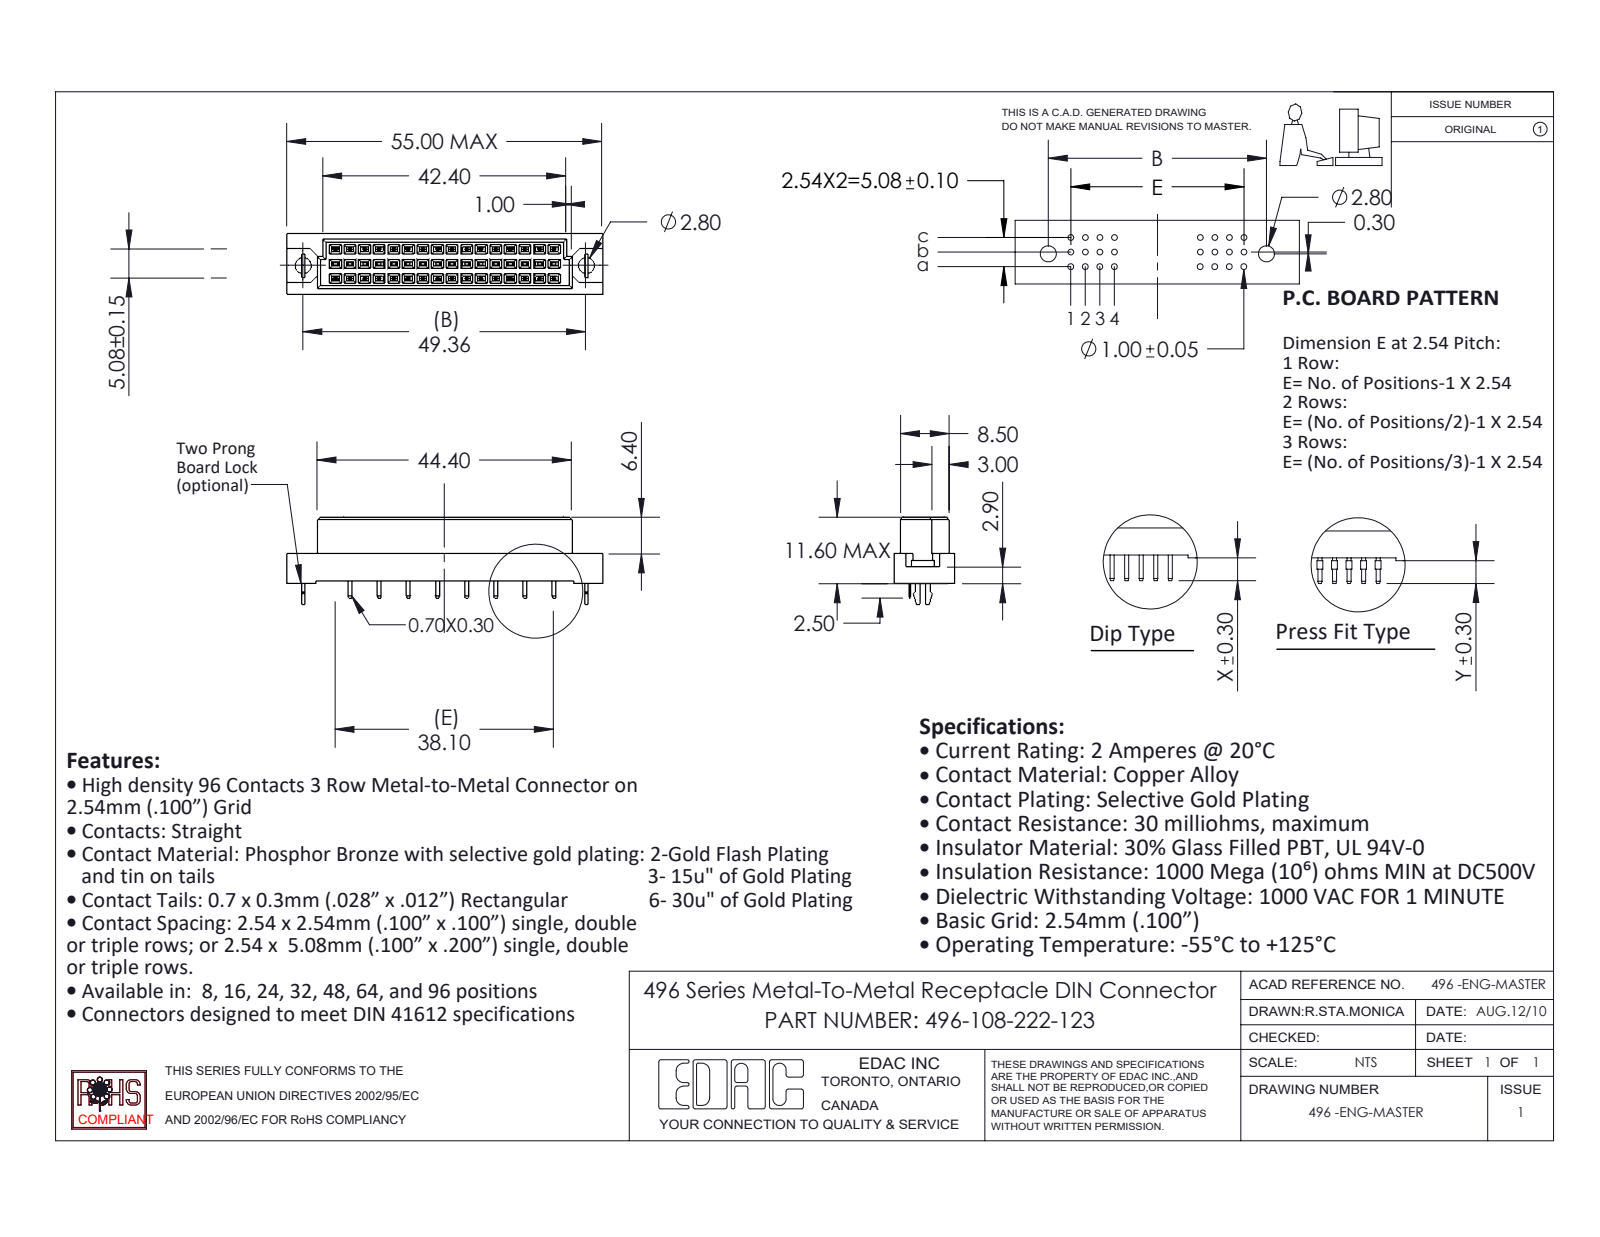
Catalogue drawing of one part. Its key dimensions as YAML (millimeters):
part_name: "496 Part_48; 496-108-222-123; 496-290_22; 496 Bore-lock"
step_written_by: "SolidWorks 2020 (CONFIG_CONTROL_DESIGN)"
units: millimeters
bodies: {solids: 11, faces: 782, planar: 776, cylindrical: 6, other: 0}
overall_size: [55, 15.2, 10.6]
volume: 4624
surface_area: 4447
round_holes:
  - {diameter: 2.8, count: 2}
partial_cylinders:
  - {radius: 0.53, count: 1}
face_to_face_distances: [2.54, 1.05, 9.55, 5.08, 0.81, 10.6, 3.35, 1.73, 8.5, 0.56]
hole_center_spacings: [49.36]
